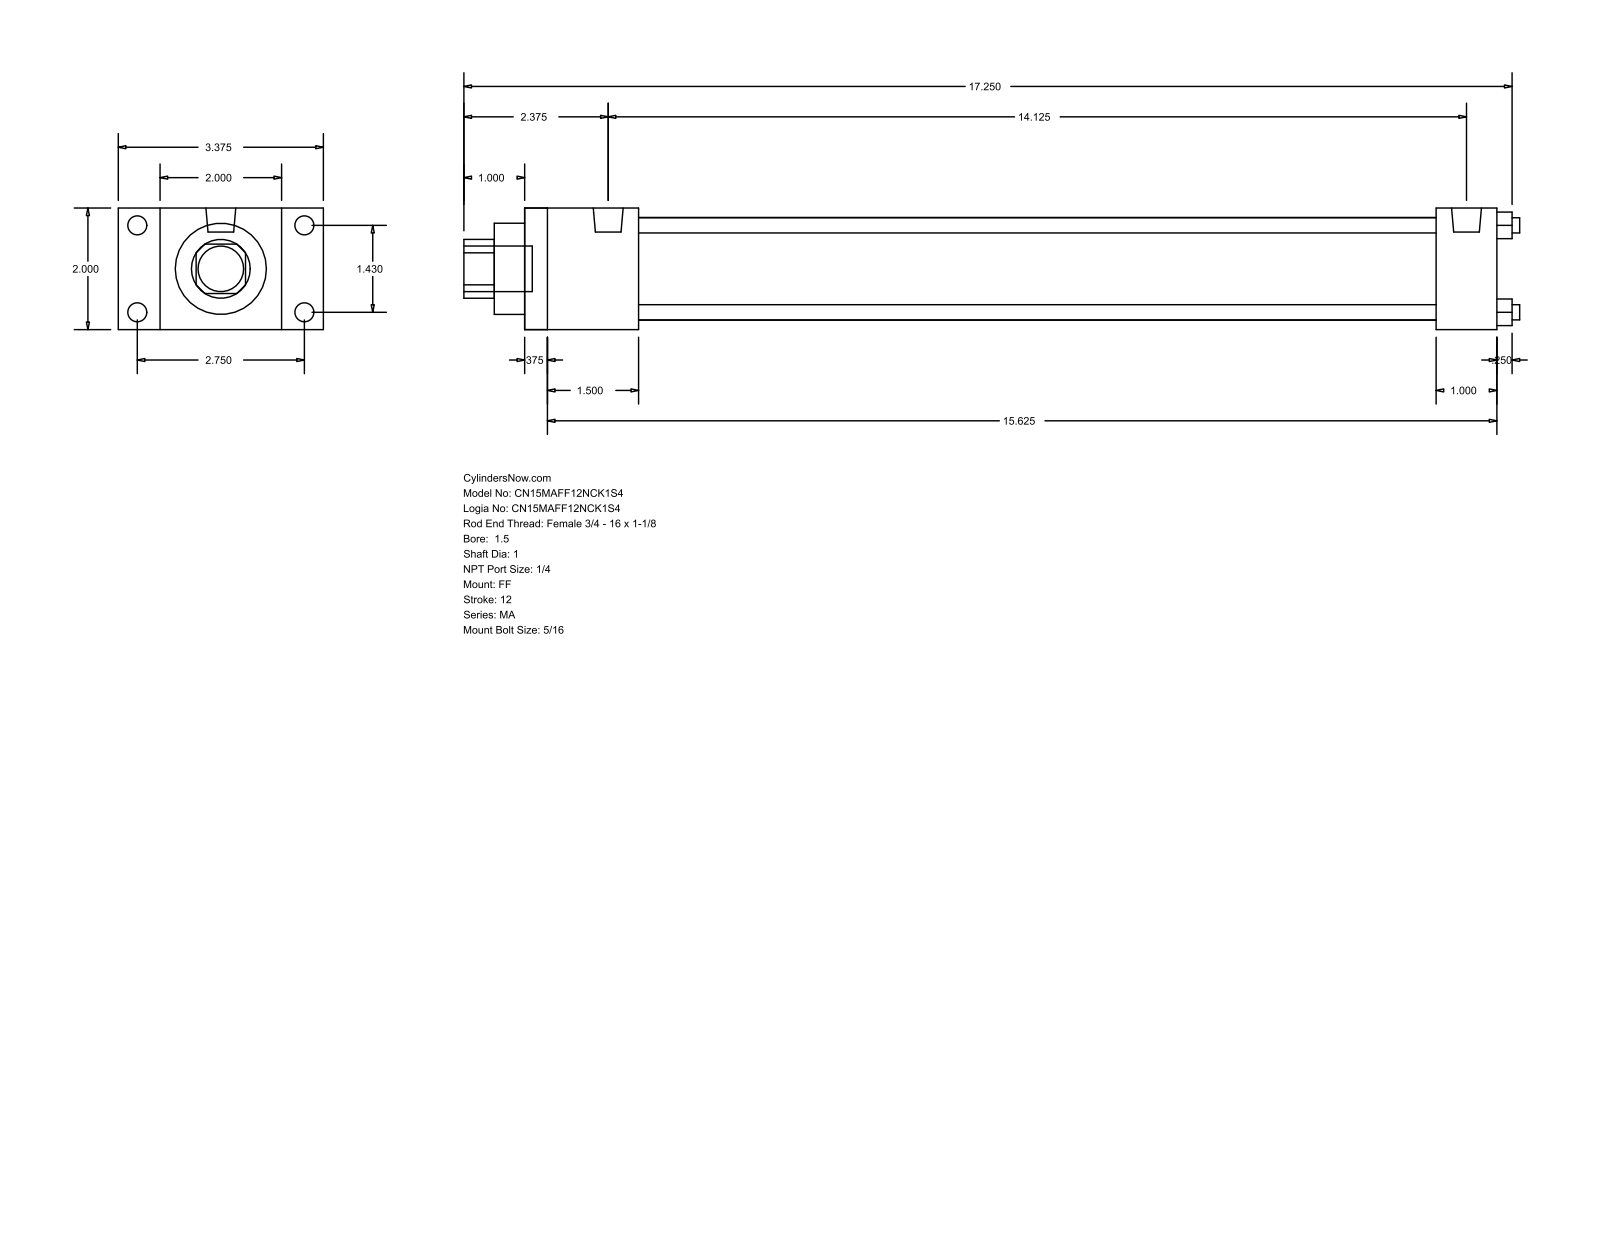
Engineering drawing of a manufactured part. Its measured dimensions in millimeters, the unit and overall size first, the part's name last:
Units: millimetres
Overall size (bounding box): 441.32 × 85.72 × 50.8
Round holes (diameter × count): ⌀6.35 ×4, ⌀25.4 ×1, ⌀38.1 ×1, ⌀42.93 ×1
Round bosses / shafts (diameter × count): ⌀7.94 ×8, ⌀12.49 ×2, ⌀19.05 ×1
Partial cylindrical surfaces — rounded edges, fillets, slot ends (radius × count): R12.29 ×1
Main face-to-face distances: 50.8, 406.4, 9.52, 396.88, 25.4, 47.63, 381, 38.11, 371.48, 333.37
Hole centre spacings: 25.68, 36.32, 51.36
Bodies: 0 solids, 92 faces (64 planar, 28 cylindrical, 0 other)
Part name (STEP PRODUCT): MA_FF__0150_1
STEP written by: GSSL Pune (CONFIG_CONTROL_DESIGN)
